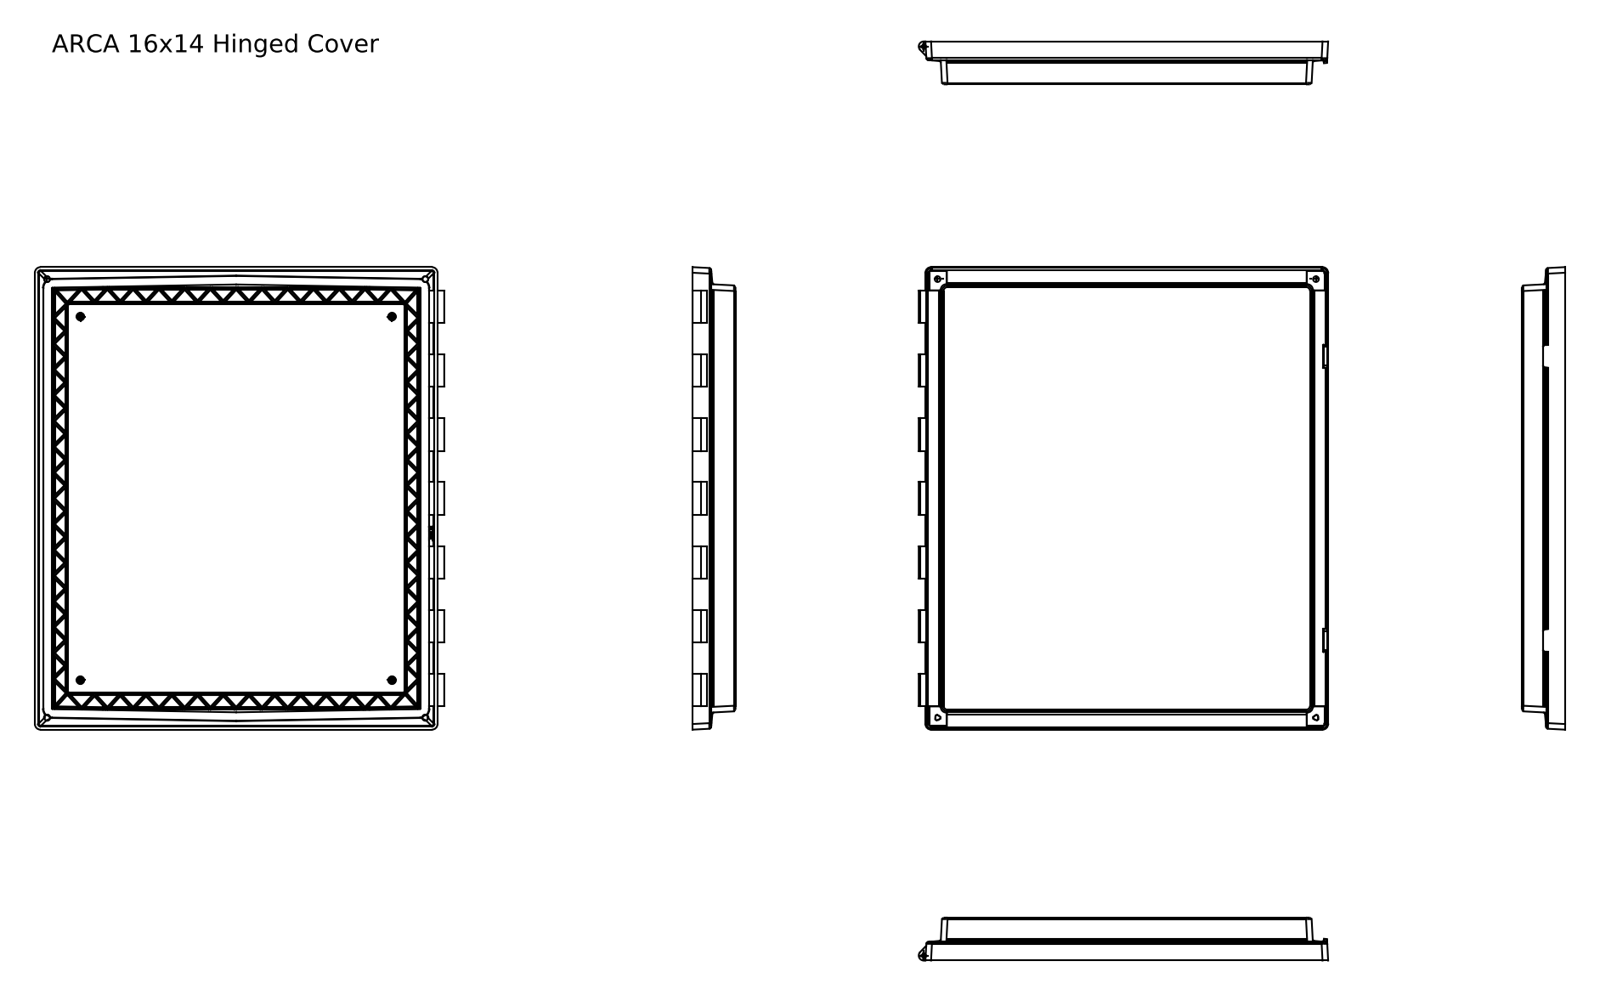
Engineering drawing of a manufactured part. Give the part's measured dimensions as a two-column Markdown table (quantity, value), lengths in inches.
| quantity | value |
| --- | --- |
| part name | 16x14_hinge_cover |
| STEP written by | SolidWorks 2008 (AUTOMOTIVE_DESIGN) |
| units | inches |
| bodies | 1 solid, 979 faces (689 planar, 174 cylindrical, 116 other) |
| overall size | 17.809 × 15.763 × 1.654 |
| volume | 69.08 in³ |
| surface area | 1 026 in² |
| round holes (diameter × count) | 0.15 × 1 |
| partial cylindrical surfaces (radius × count) | 0.039 × 12, 0.079 × 12, 0.059 × 4, 0.098 × 4, 0.217 × 4, 0.346 × 4, 0.906 × 4, 1.043 × 4 |
| main face-to-face distances | 0.142, 0.118, 0.731, 2.104, 2.925, 13.052, 2.194, 1.403, 0.702, 0.131 |
